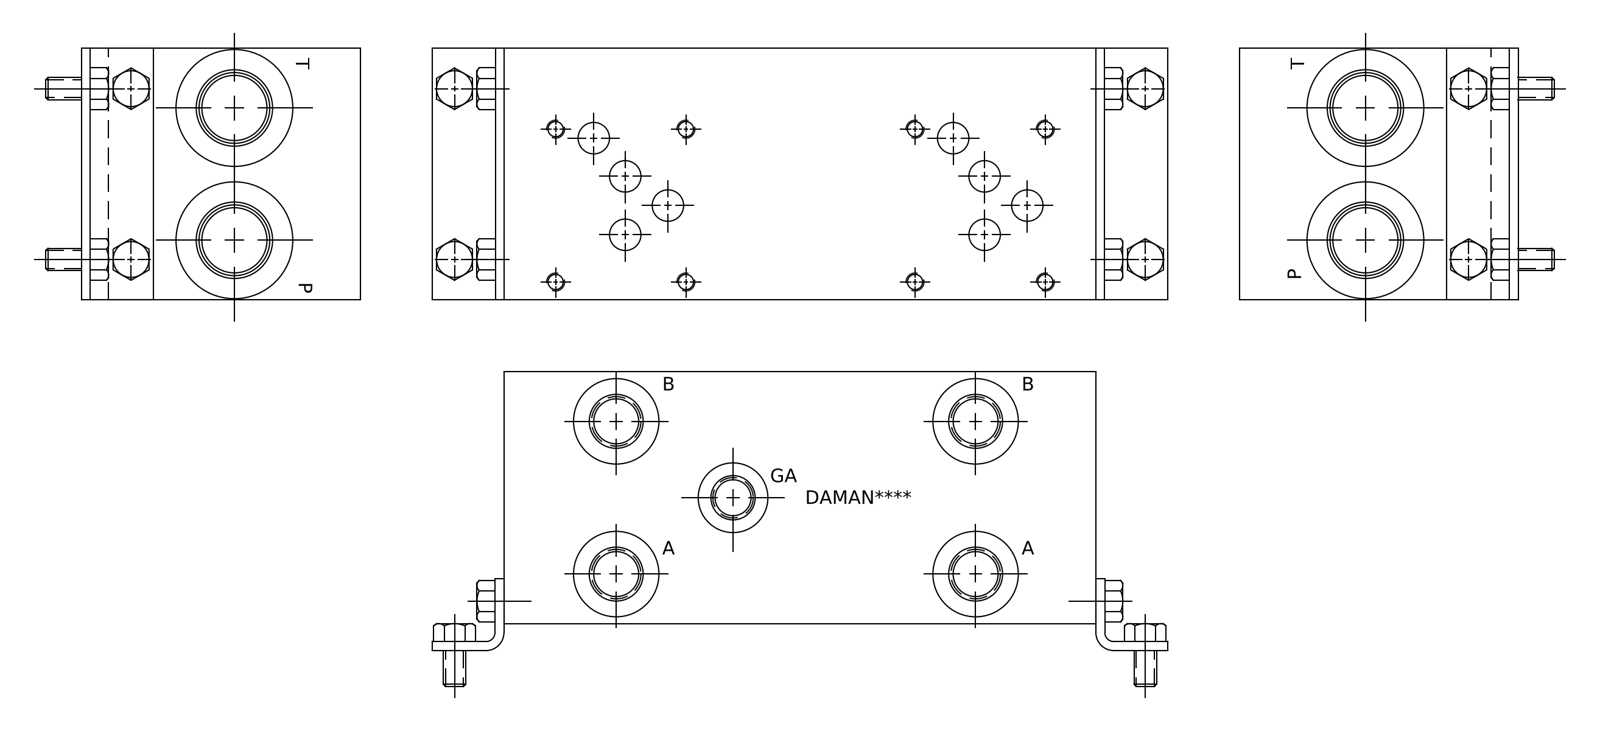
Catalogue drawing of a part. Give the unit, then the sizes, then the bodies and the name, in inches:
Units: inches
Overall size (bounding box): 8.25 × 3.5 × 3.5
Round holes (diameter × count): ⌀0.201 ×8, ⌀0.25 ×8, ⌀0.438 ×8, ⌀0.625 ×4, ⌀0.689 ×4, ⌀0.75 ×4, ⌀0.758 ×4, ⌀1.206 ×4, ⌀0.257 ×2, ⌀0.312 ×2, ⌀0.906 ×2, ⌀0.981 ×2
Main face-to-face distances: 3.5, 8.25, 0.031, 8.219, 3.469, 8.188, 0.75, 0.781, 7.469, 7.438
Hole centre spacings: 5, 1.813, 2.793, 1.171, 2.125, 5.433, 0.546, 0.719
Volume: 94.1 in³ · Surface area: 174.7 in²
Bodies: 1 solid, 643 faces (351 planar, 77 cylindrical, 215 other)
Part name (STEP PRODUCT): Part_AD05P025S_3D
STEP written by: Autodesk Inventor 2020 (AUTOMOTIVE_DESIGN)
